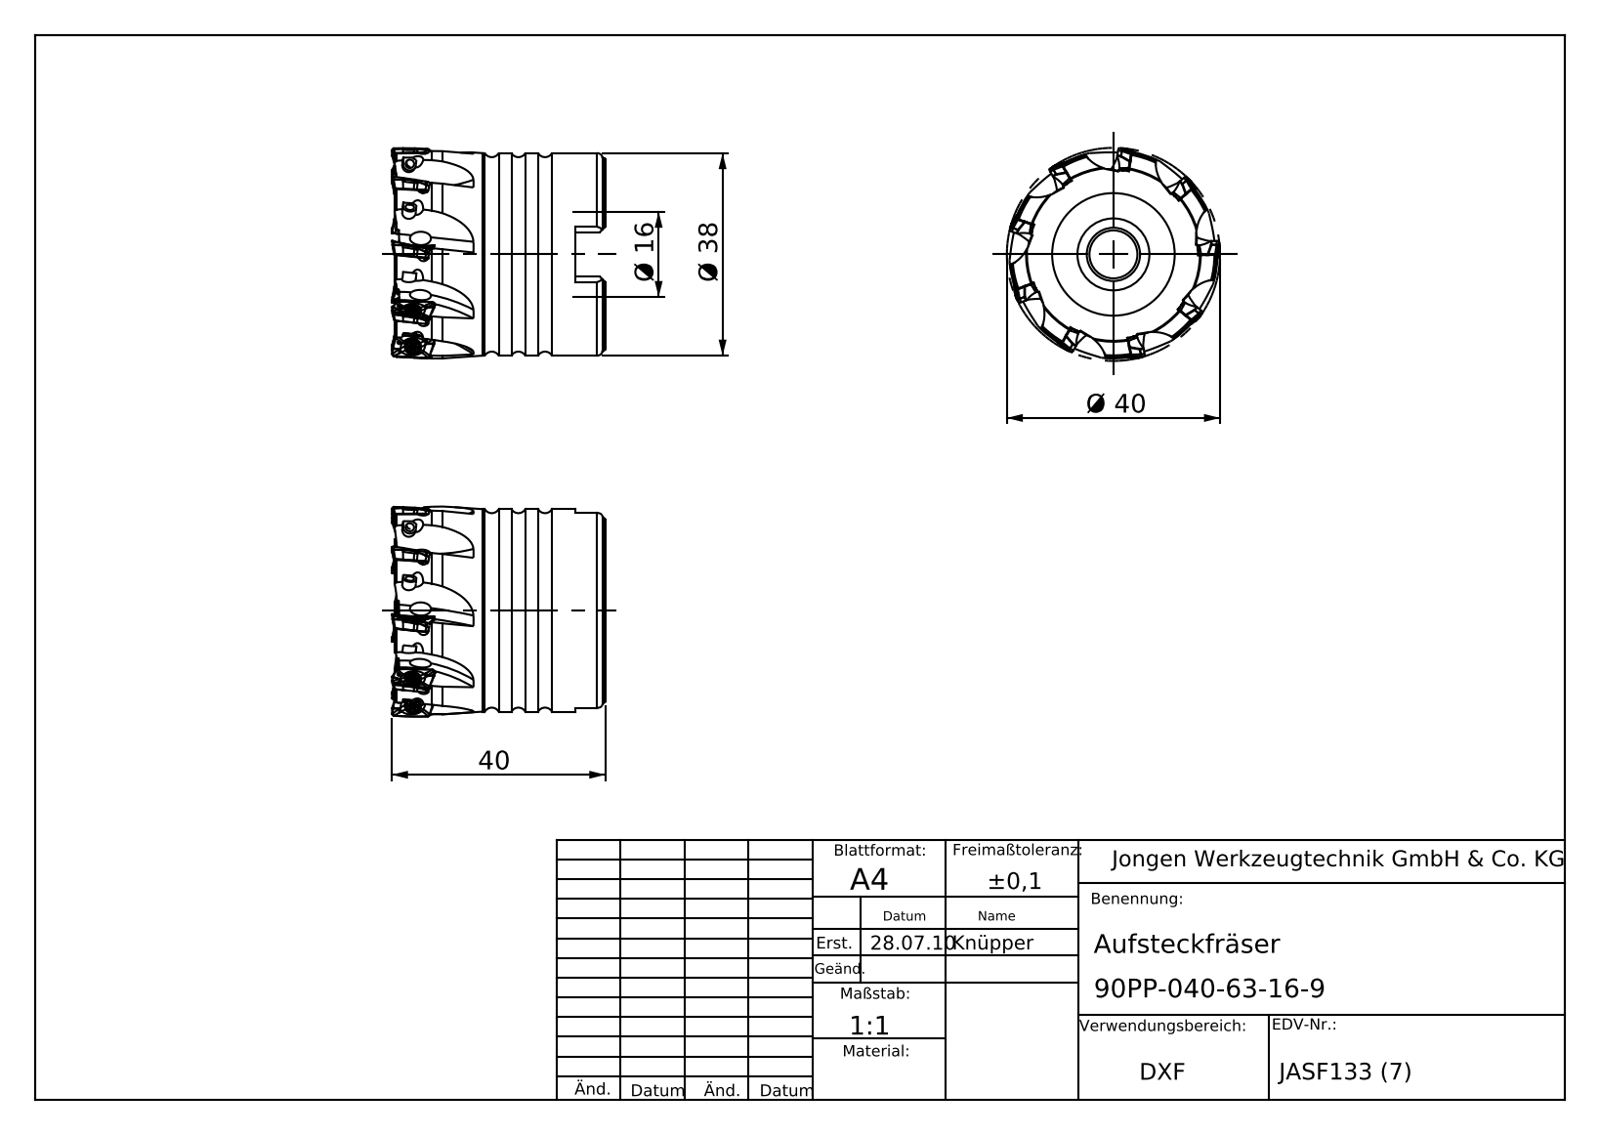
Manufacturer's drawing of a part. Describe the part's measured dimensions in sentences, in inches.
The part is named "90PP-040-63-16-9". Its 3-D file was written by "SolidWorks 2011 (AUTOMOTIVE_DESIGN)". It is 1 solid with 224 faces: 73 planar, 55 cylindrical and 96 other. Overall it measures 1.575 by 1.575 by 1.575 inches. Its volume is 2.16 cubic inches and its surface area 17.17 square inches. Round holes: 9 of diameter 0.098, 1 of diameter 0.354, 1 of diameter 0.531, 1 of diameter 0.63, 1 of diameter 0.636, 1 of diameter 0.642. Round bosses or shafts: 1 of diameter 1.496. Partial cylindrical surfaces (rounded edges, fillets, slot ends): 9 of radius 0.787, 1 of radius 0.769. The main face-to-face distances are 1.502, 0.22, 1.281, 1.555, 1.335, 0.053, 0.331, 1.069, 0.848, 0.433.
